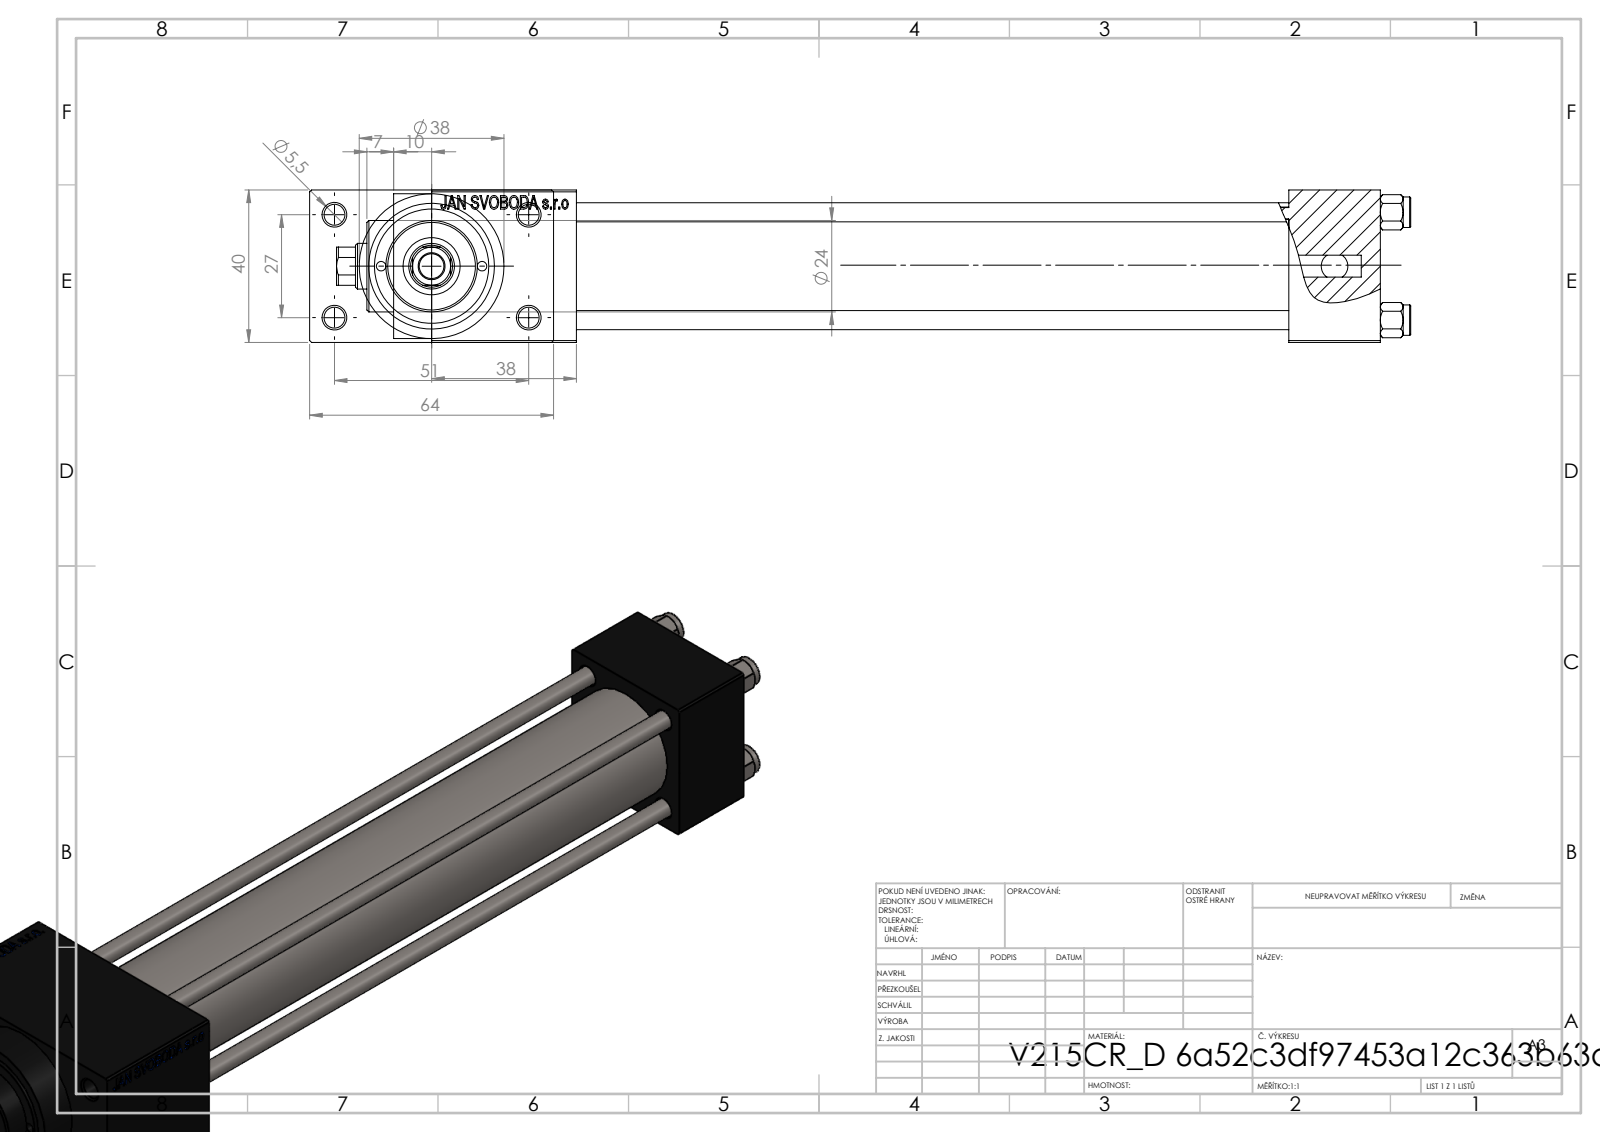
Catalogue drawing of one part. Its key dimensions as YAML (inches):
part_name: "NUT_M5_D; V215_VC_A; V215CR_VCP_D; V215CR_D_Body (+1 more)"
step_written_by: "SolidWorks 2019 (CONFIG_CONTROL_DESIGN)"
units: inches
bodies: {solids: 11, faces: 1110, planar: 498, cylindrical: 92, other: 520}
overall_size: [11.102, 2.52, 1.575]
volume: 14.48
surface_area: 156.3
round_holes:
  - {diameter: 0.197, count: 4}
  - {diameter: 0.217, count: 4}
  - {diameter: 0.787, count: 3}
  - {diameter: 0.098, count: 2}
  - {diameter: 0.276, count: 2}
  - {diameter: 0.518, count: 2}
  - {diameter: 0.256, count: 1}
  - {diameter: 0.472, count: 1}
  - {diameter: 0.591, count: 1}
  - {diameter: 0.984, count: 1}
  - {diameter: 1.181, count: 1}
round_bosses_or_shafts:
  - {diameter: 0.315, count: 4}
  - {diameter: 1.496, count: 1}
  - {diameter: 1.22, count: 1}
  - {diameter: 0.945, count: 1}
partial_cylinders:
  - {radius: 0.217, count: 1}
face_to_face_distances: [1.575, 0.472, 7.362, 0.945, 8.307, 2.047, 1.496, 9.803, 8.858, 2.52]
hole_center_spacings: [0.448, 0.558, 0.718, 0.788, 1.114, 1.136, 1.177, 1.214]
